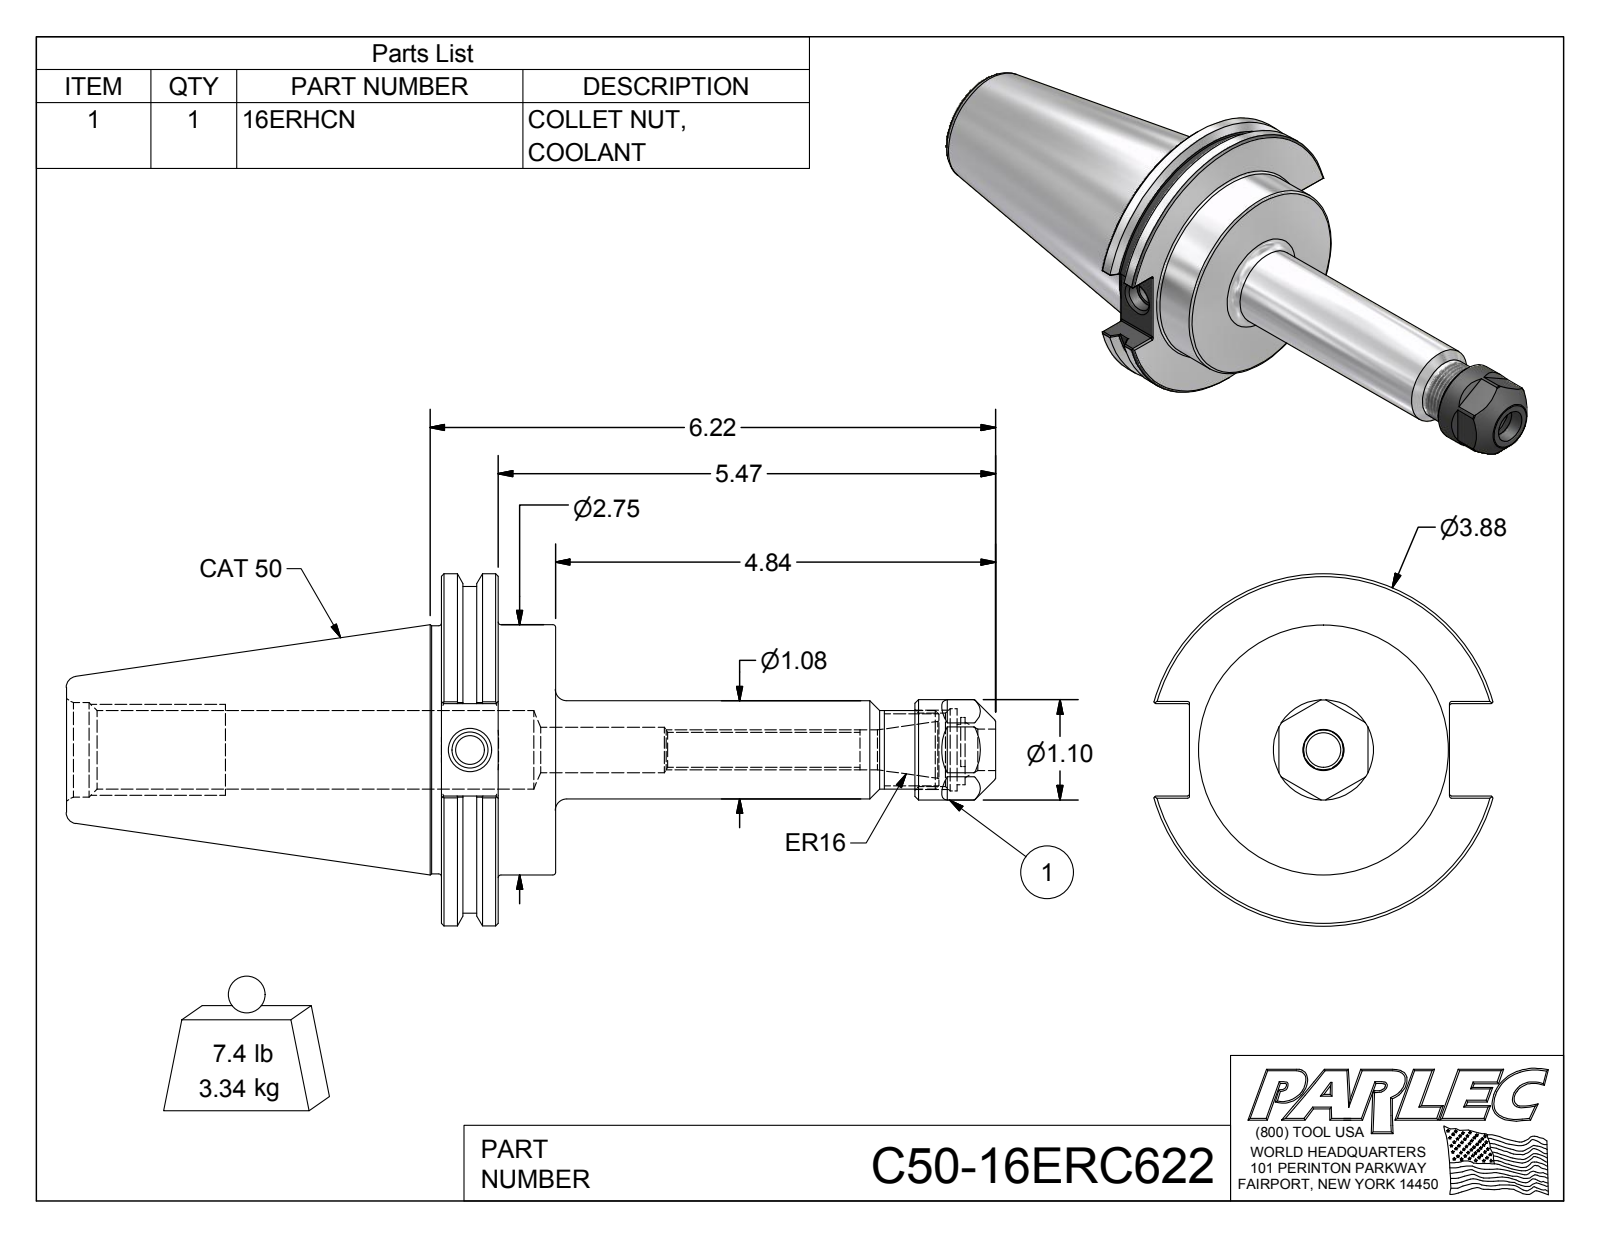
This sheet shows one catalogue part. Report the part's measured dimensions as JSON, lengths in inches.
{"part_name": "C50-16ERC622; C50-16ER6-1; 16ERHCN", "step_written_by": "Autodesk Inventor 2012 (AUTOMOTIVE_DESIGN)", "units": "inches", "bodies": {"solids": 2, "faces": 130, "planar": 50, "cylindrical": 35, "other": 45}, "overall_size": [10.22, 3.875, 3.729], "volume_in3": 26.17, "surface_area_in2": 100.7, "round_holes": [[0.315, 1], [0.383, 1], [0.399, 1], [0.44, 1], [0.453, 1], [0.5, 1], [0.661, 1], [0.807, 1], [0.865, 1], [0.906, 1], [1.038, 1]], "round_bosses_or_shafts": [[3.875, 1], [3.594, 1], [2.75, 1], [2.73, 1], [1.102, 1], [1.08, 1], [0.866, 1]], "partial_cylinders_radius": [[0.02, 12], [0.354, 1]], "face_to_face_distances": [1.255, 0.625, 0.63, 0.979, 4.125, 4.75, 5.38, 2.86, 1.015, 0.866], "hole_center_spacings": [0.051]}
